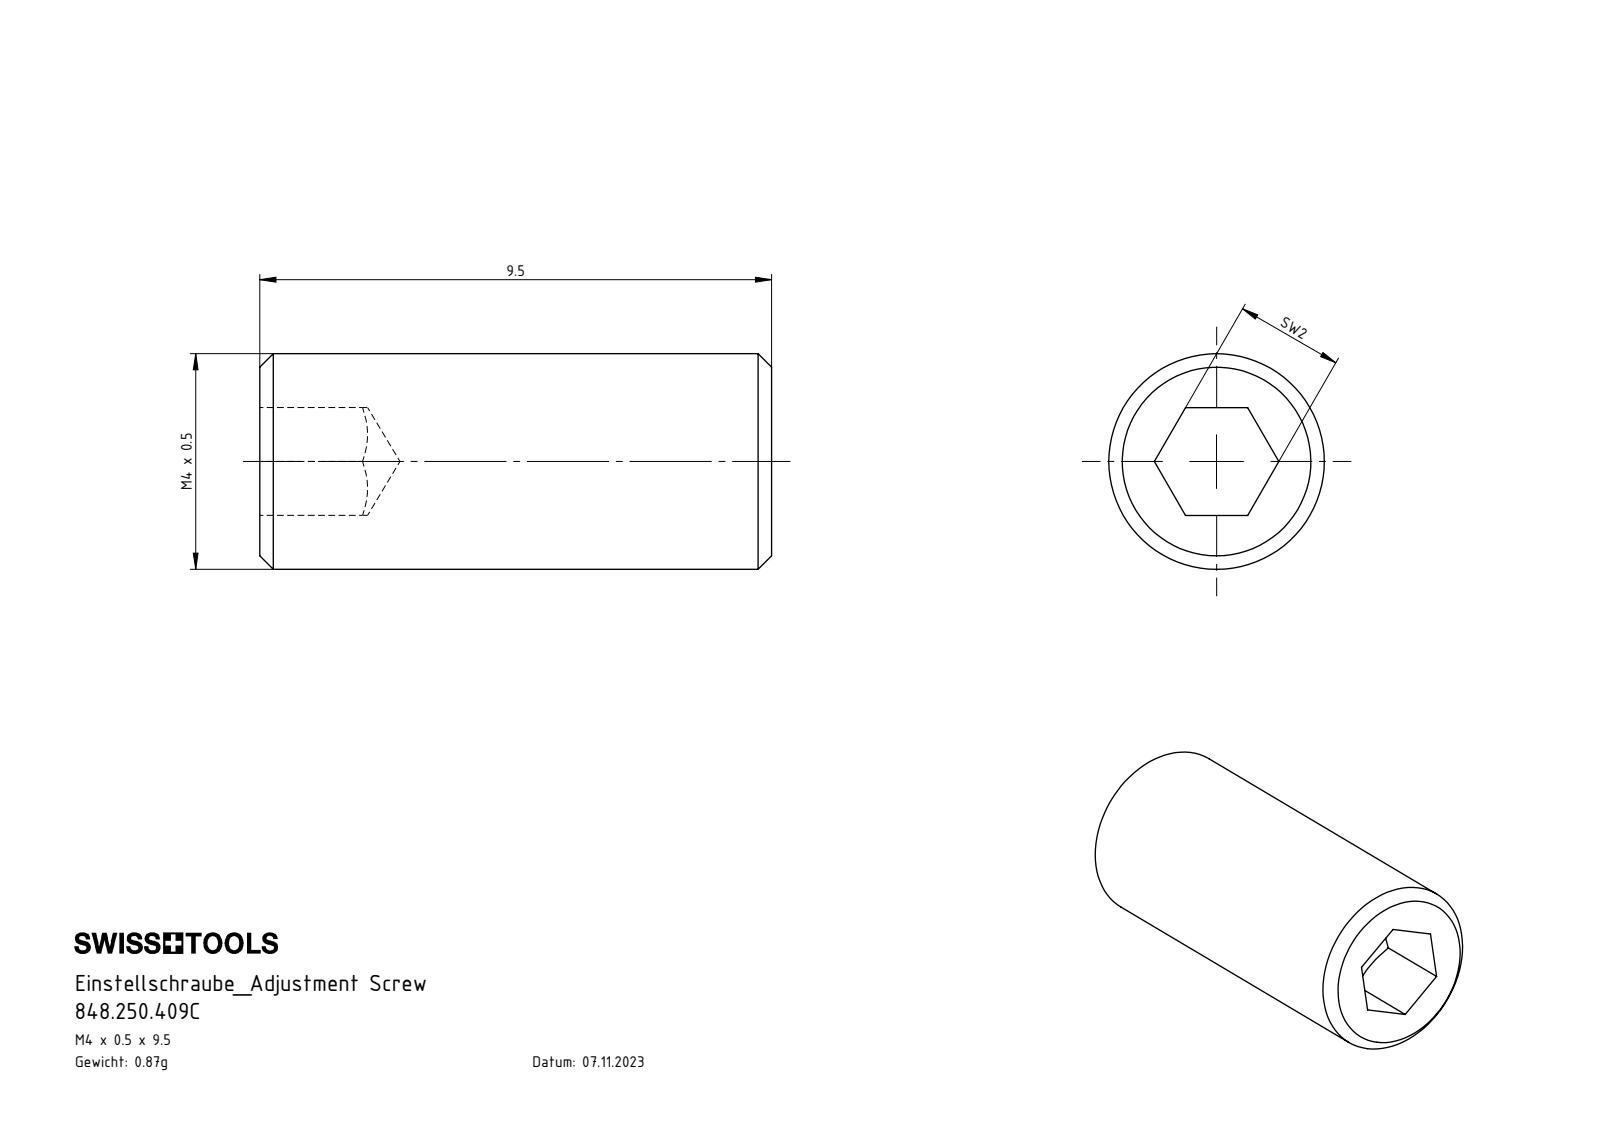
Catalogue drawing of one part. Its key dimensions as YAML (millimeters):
part_name: "848.250.409C"
step_written_by: "SolidWorks 2022 (AUTOMOTIVE_DESIGN)"
units: millimeters
bodies: {solids: 1, faces: 16, planar: 8, cylindrical: 2, other: 6}
overall_size: [9.5, 4, 4]
volume: 111
surface_area: 155
round_bosses_or_shafts:
  - {diameter: 4, count: 1}
face_to_face_distances: [2, 9.5]
